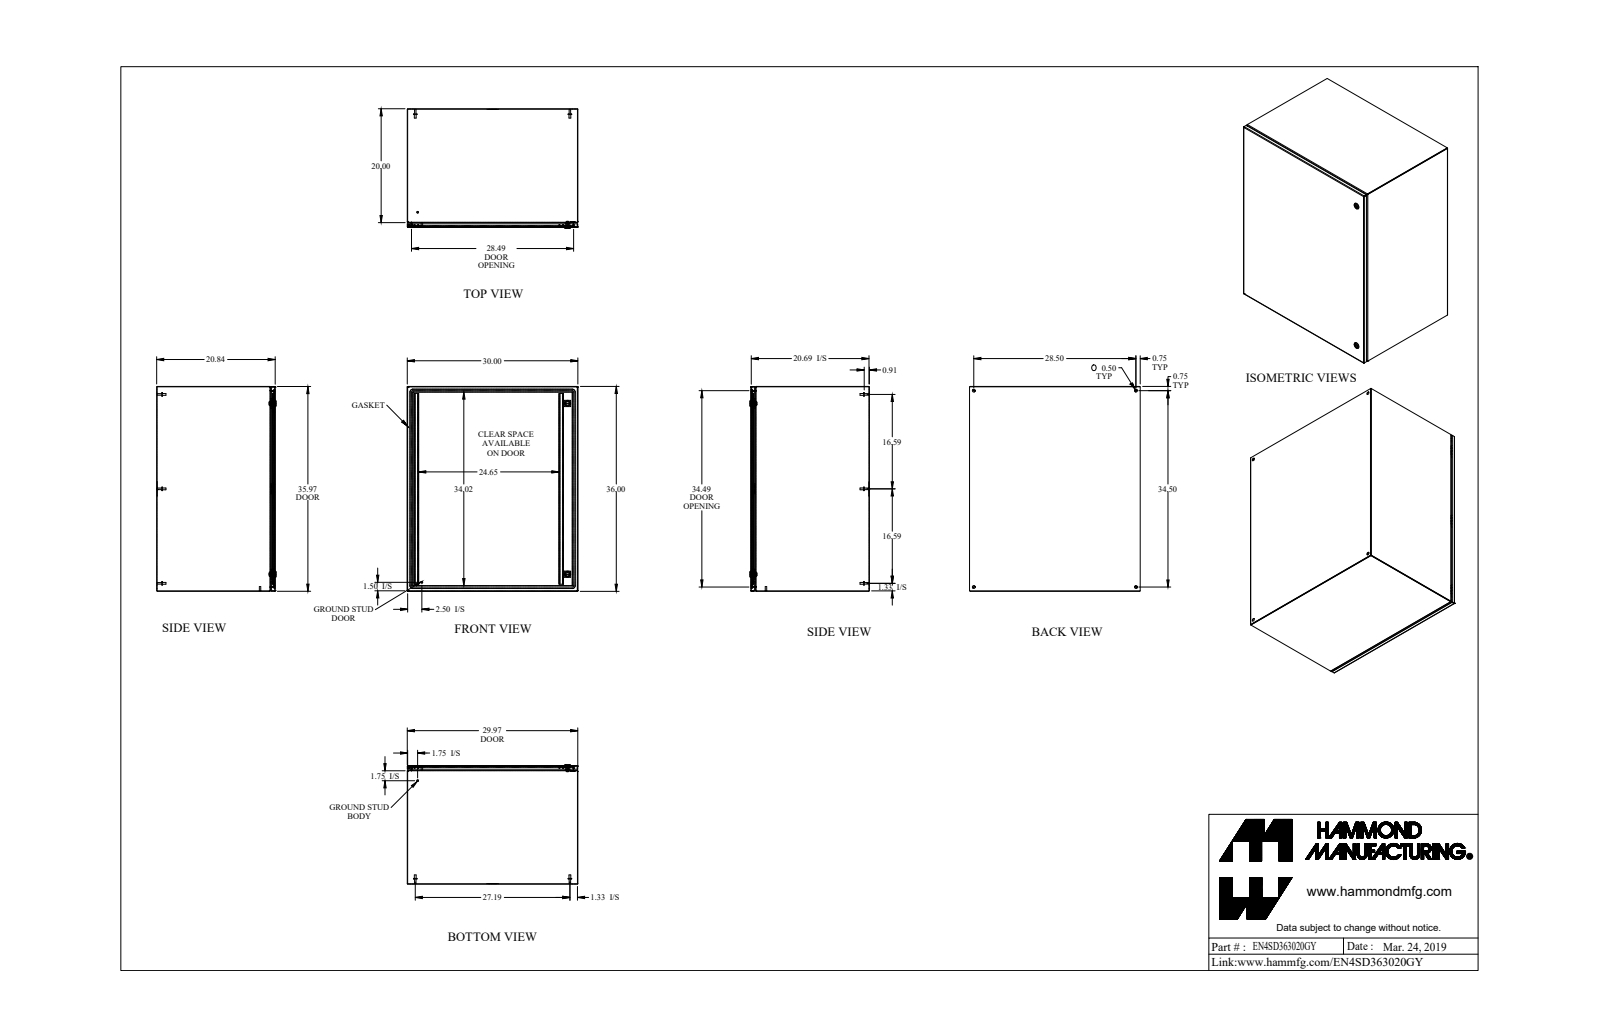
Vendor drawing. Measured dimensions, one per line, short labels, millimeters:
name: EN4SD363020GY
written by: SolidWorks 2019 (AUTOMOTIVE_DESIGN)
unit: mm
bodies: 35 solids, 901 faces (434 planar, 295 cylindrical, 172 other)
size: 914.4 × 762 × 533.3
volume: 6 243 000 mm³; area: 6 881 000 mm²
holes: 4× ⌀12.7, 2× ⌀5.9, 2× ⌀15.9, 2× ⌀19.9, 1× ⌀4.4, 1× ⌀6.1, 1× ⌀6.1
bosses: 6× ⌀15.9, 6× ⌀8, 6× ⌀6.9, 2× ⌀27.9, 2× ⌀13.3, 2× ⌀7.1, 2× ⌀6.4, 1× ⌀11.6
rounds: 18× R0.9, 18× R2.7, 12× R1.1, 12× R2.1, 12× R7.9, 6× R0.2, 6× R1.6, 4× R3.2
face distances: 1.8, 527.4, 760.2, 912.6, 525.6, 529.3, 758.3, 762, 910.7, 914.4
hole spacings: 699, 723.9, 876.3, 1136.6, 63.3, 63.3, 762, 819.6
